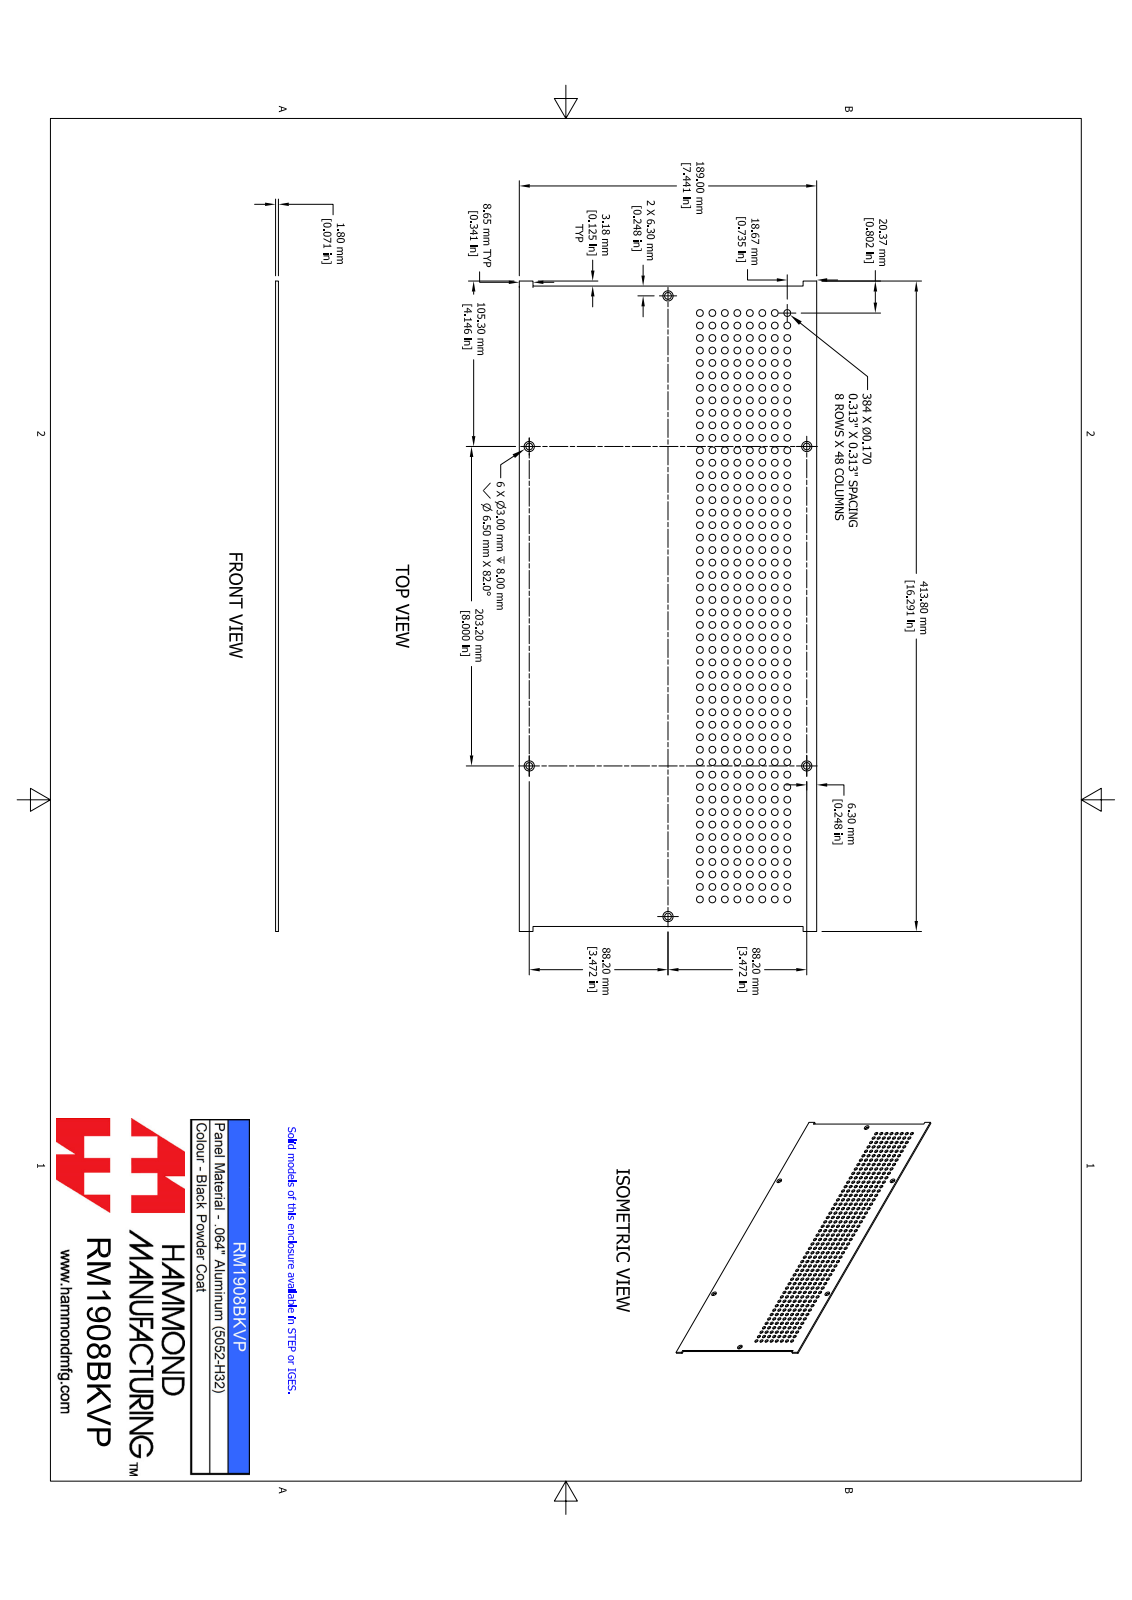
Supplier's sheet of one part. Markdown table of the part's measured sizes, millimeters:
| quantity | value |
| --- | --- |
| part name | RM1908BKVP |
| STEP written by | SolidWorks 2021 (AUTOMOTIVE_DESIGN) |
| units | millimeters |
| bodies | 1 solid, 410 faces (14 planar, 390 cylindrical, 6 other) |
| overall size | 413.8 × 189 × 1.8 |
| volume | 128 500 mm³ |
| surface area | 154 500 mm² |
| round holes (diameter × count) | 4.3 × 384, 4.3 × 6 |
| main face-to-face distances | 1.8, 189, 407.4, 410.6, 3.2, 3.2, 410.6, 413.8, 8.7, 180.3 |
| hole center spacings | 17.8, 8, 15.9, 25.1, 32.7, 7.9, 11.2, 17.7 |
